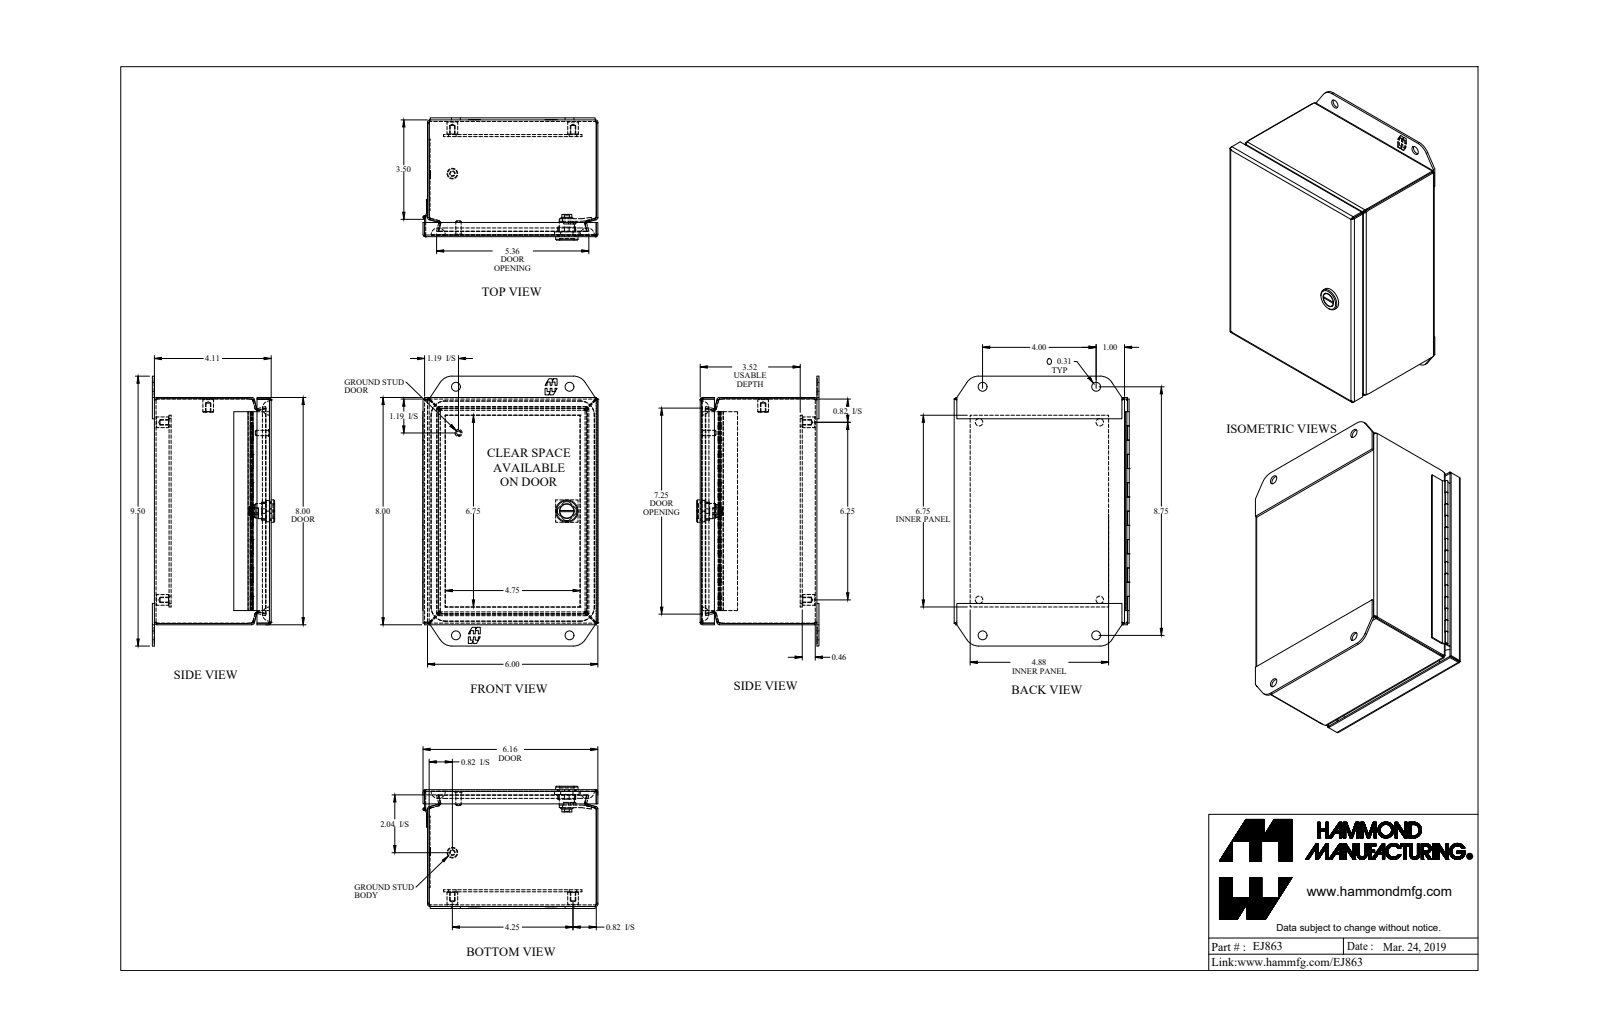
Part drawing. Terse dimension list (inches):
name: EJ863_Default
written by: SolidWorks 2019 (CONFIG_CONTROL_DESIGN)
unit: in
bodies: 16 solids, 643 faces (361 planar, 190 cylindrical, 92 other)
size: 9.5 × 6.165 × 4.305
volume: 19.37 in³; area: 636.6 in²
holes: 5× ⌀0.156, 4× ⌀0.265, 4× ⌀0.313, 1× ⌀0.05, 1× ⌀0.516
bosses: 5× ⌀0.375, 1× ⌀0.788, 1× ⌀0.535, 1× ⌀0.496, 1× ⌀0.435, 1× ⌀0.25, 1× ⌀0.188, 1× ⌀0.1
rounds: 16× R0.029, 16× R0.086, 10× R0.281, 4× R0.25, 4× R0.499, 4× R0.5, 2× R0.06, 2× R0.539
face distances: 0.057, 4.054, 5.943, 0.072, 0.589, 4.111, 3.997, 7.943, 0.46, 0.517
hole spacings: 1.256, 4.31, 7.502, 8.56, 3.133, 4, 4.25, 4.376
